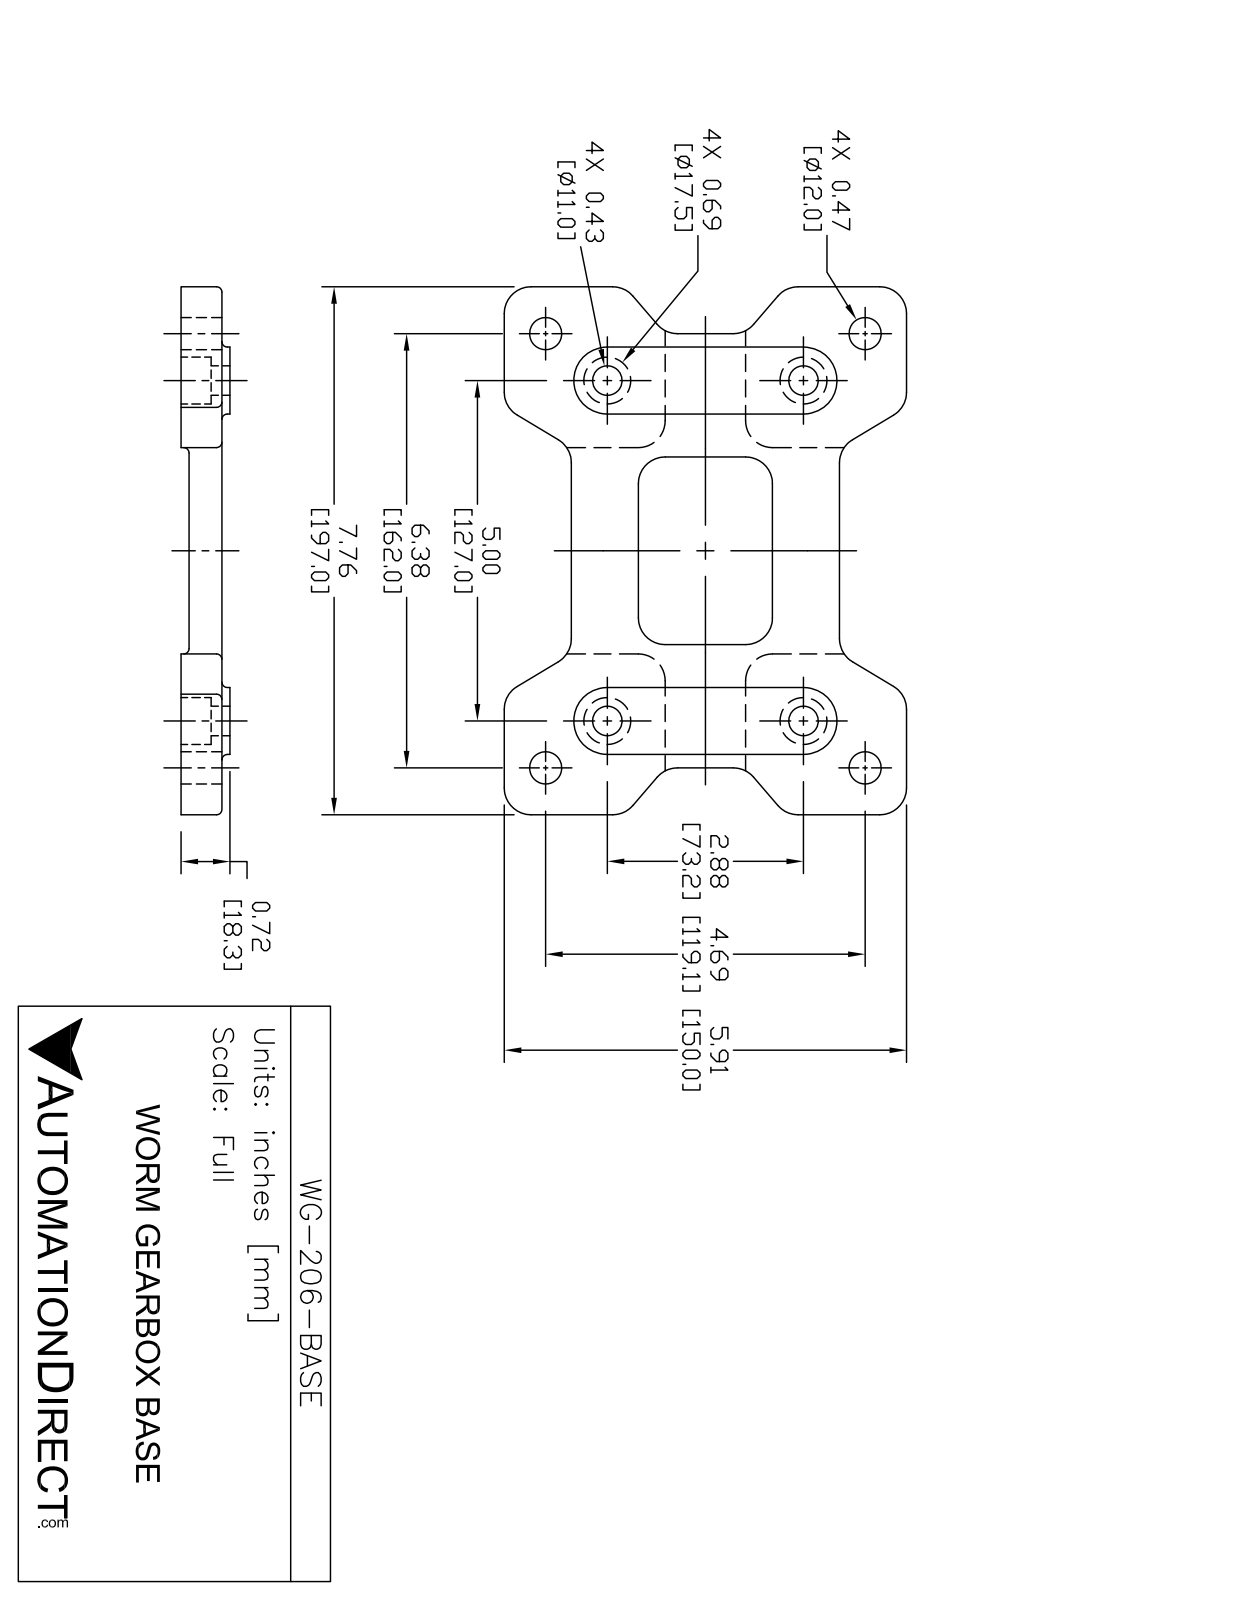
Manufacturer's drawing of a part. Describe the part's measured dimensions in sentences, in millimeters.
The part is named "WG-206-BASE". Its 3-D file was written by "SolidWorks 2017 (AUTOMOTIVE_DESIGN)". It is 1 solid with 128 faces: 48 planar, 70 cylindrical and 10 other. Overall it measures 197 by 150 by 18.3 millimeters. Its volume is 277 300 cubic millimeters and its surface area 59 270 square millimeters. Round holes: 4 of diameter 11, 4 of diameter 12, 4 of diameter 17.5. Partial cylindrical surfaces (rounded edges, fillets, slot ends): 24 of radius 10, 4 of radius 1, 4 of radius 2, 4 of radius 8, 4 of radius 12.5. The main face-to-face distances are 15.3, 3, 12.3, 18.3, 25, 100, 50, 125, 75, 197. The hole center spacings are 28.9, 97.7, 146.3, 173.6, 73.2, 119.1, 127, 146.6.
